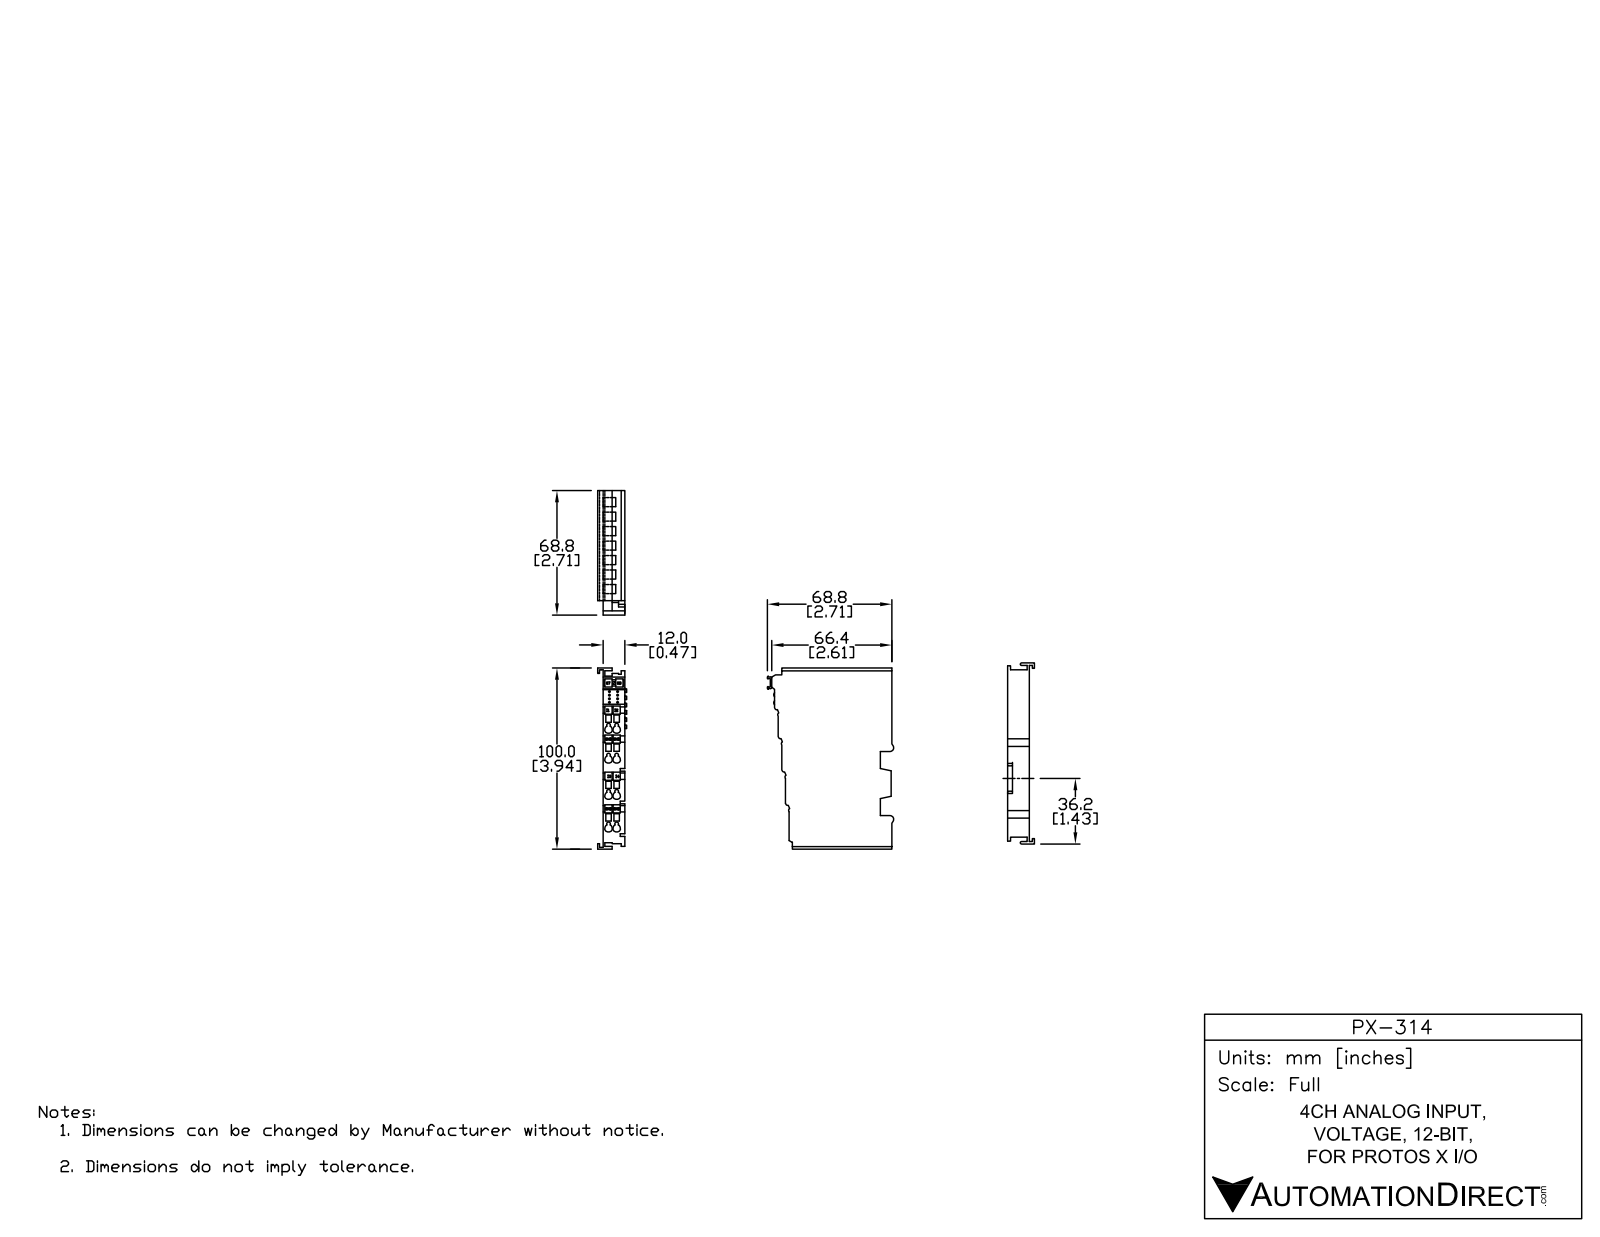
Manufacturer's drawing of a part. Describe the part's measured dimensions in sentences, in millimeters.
The part is named "PX-314". Its 3-D file was written by "SolidWorks 2014 (AUTOMOTIVE_DESIGN)". It is 26 solids with 1425 faces: 1011 planar, 354 cylindrical and 60 other. Overall it measures 100.25 by 69.28 by 15.15 millimeters. Its volume is 59 090 cubic millimeters and its surface area 32 341 square millimeters. Round holes: 8 of diameter 4. Partial cylindrical surfaces (rounded edges, fillets, slot ends): 67 of radius 0.25, 43 of radius 0.3, 12 of radius 0.38, 10 of radius 0.4, 8 of radius 1, 4 of radius 0.17, 4 of radius 1.03, 4 of radius 1.38. The main face-to-face distances are 12, 2, 10, 1, 1.85, 11, 4, 8.7, 3.15, 1.22. The hole center spacings are 5, 18.4, 19.07, 16, 16.76, 34.4, 34.76, 36.8.
